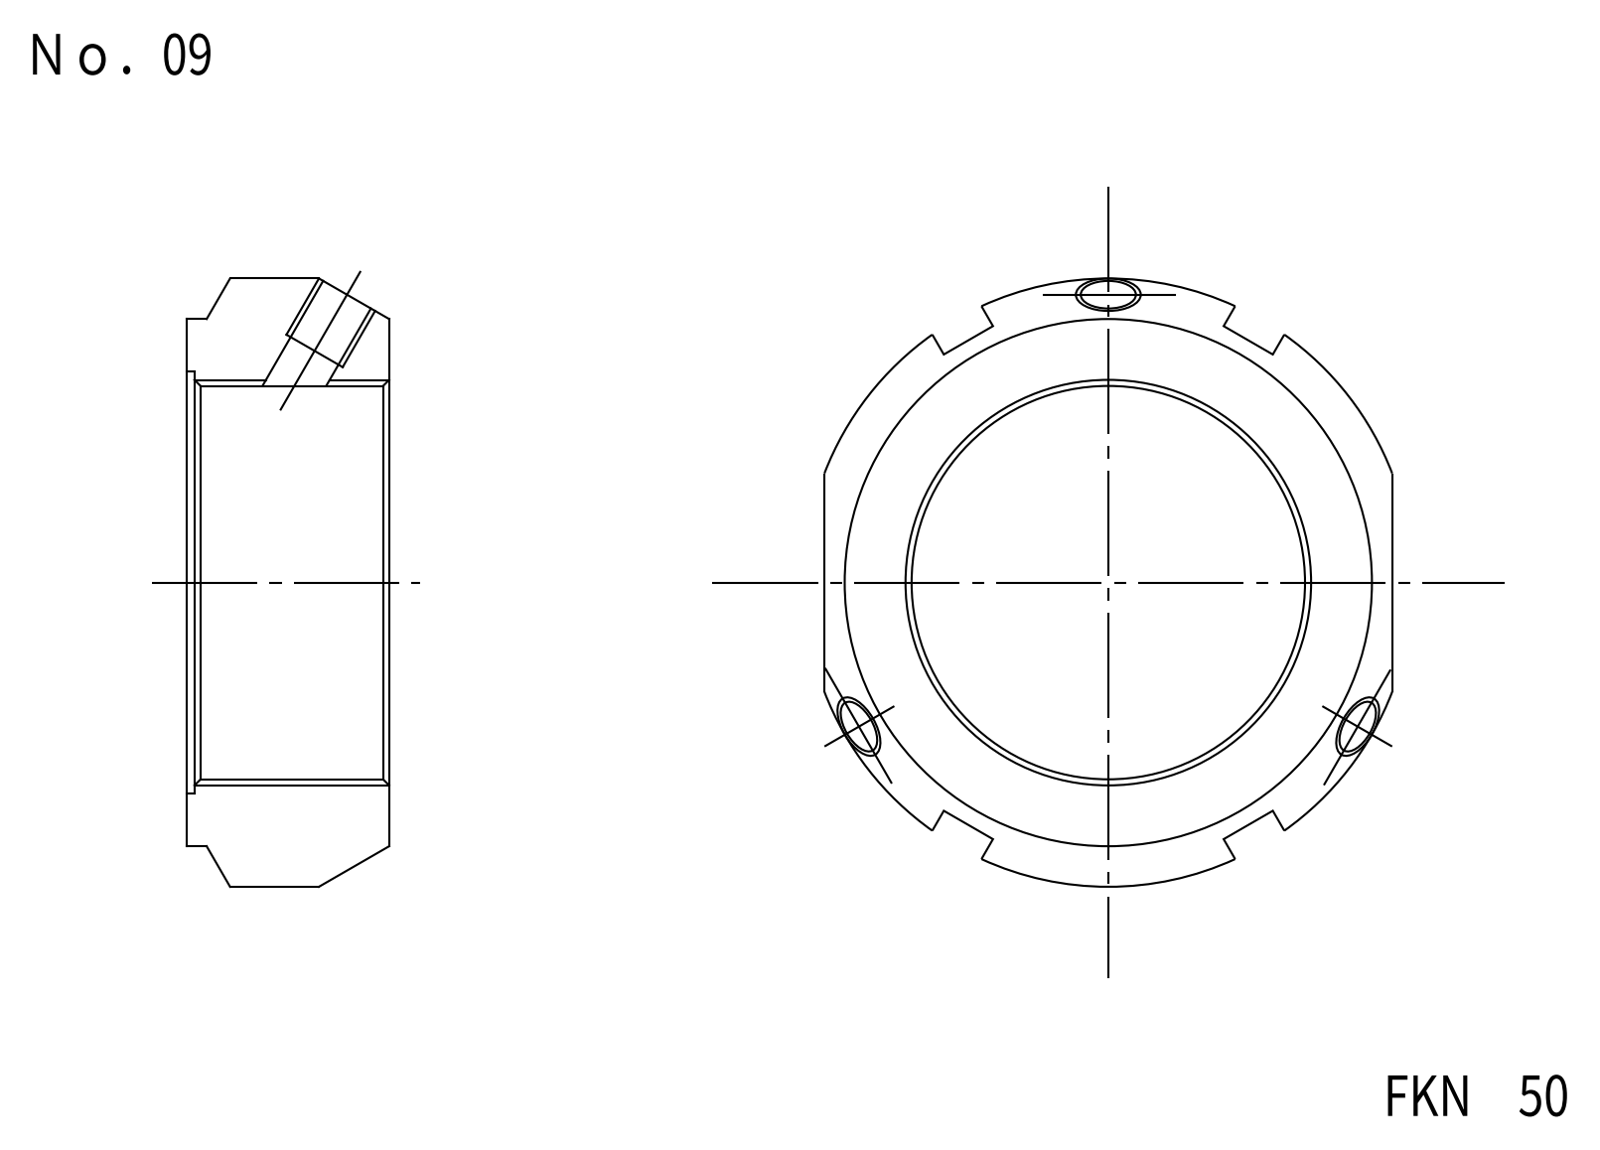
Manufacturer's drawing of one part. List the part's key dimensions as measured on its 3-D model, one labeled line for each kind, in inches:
Part name (STEP PRODUCT): FKD FKN50
STEP written by: Autodesk Inventor LT (CONFIG_CONTROL_DESIGN)
Units: inches
Bodies: 1 solid, 37 faces (20 planar, 15 cylindrical, 2 other)
Overall size (bounding box): 2.953 × 2.756 × 0.984
Volume: 2.946 in³ · Surface area: 21.5 in²
Round holes (diameter × count): ⌀0.262 ×3, ⌀0.319 ×3, ⌀1.969 ×1, ⌀2.047 ×1
Round bosses / shafts (diameter × count): ⌀2.559 ×1
Partial cylindrical surfaces — rounded edges, fillets, slot ends (radius × count): R1.476 ×1
Main face-to-face distances: 0.984, 2.756, 2.717, 0.276, 0.059, 0.925
